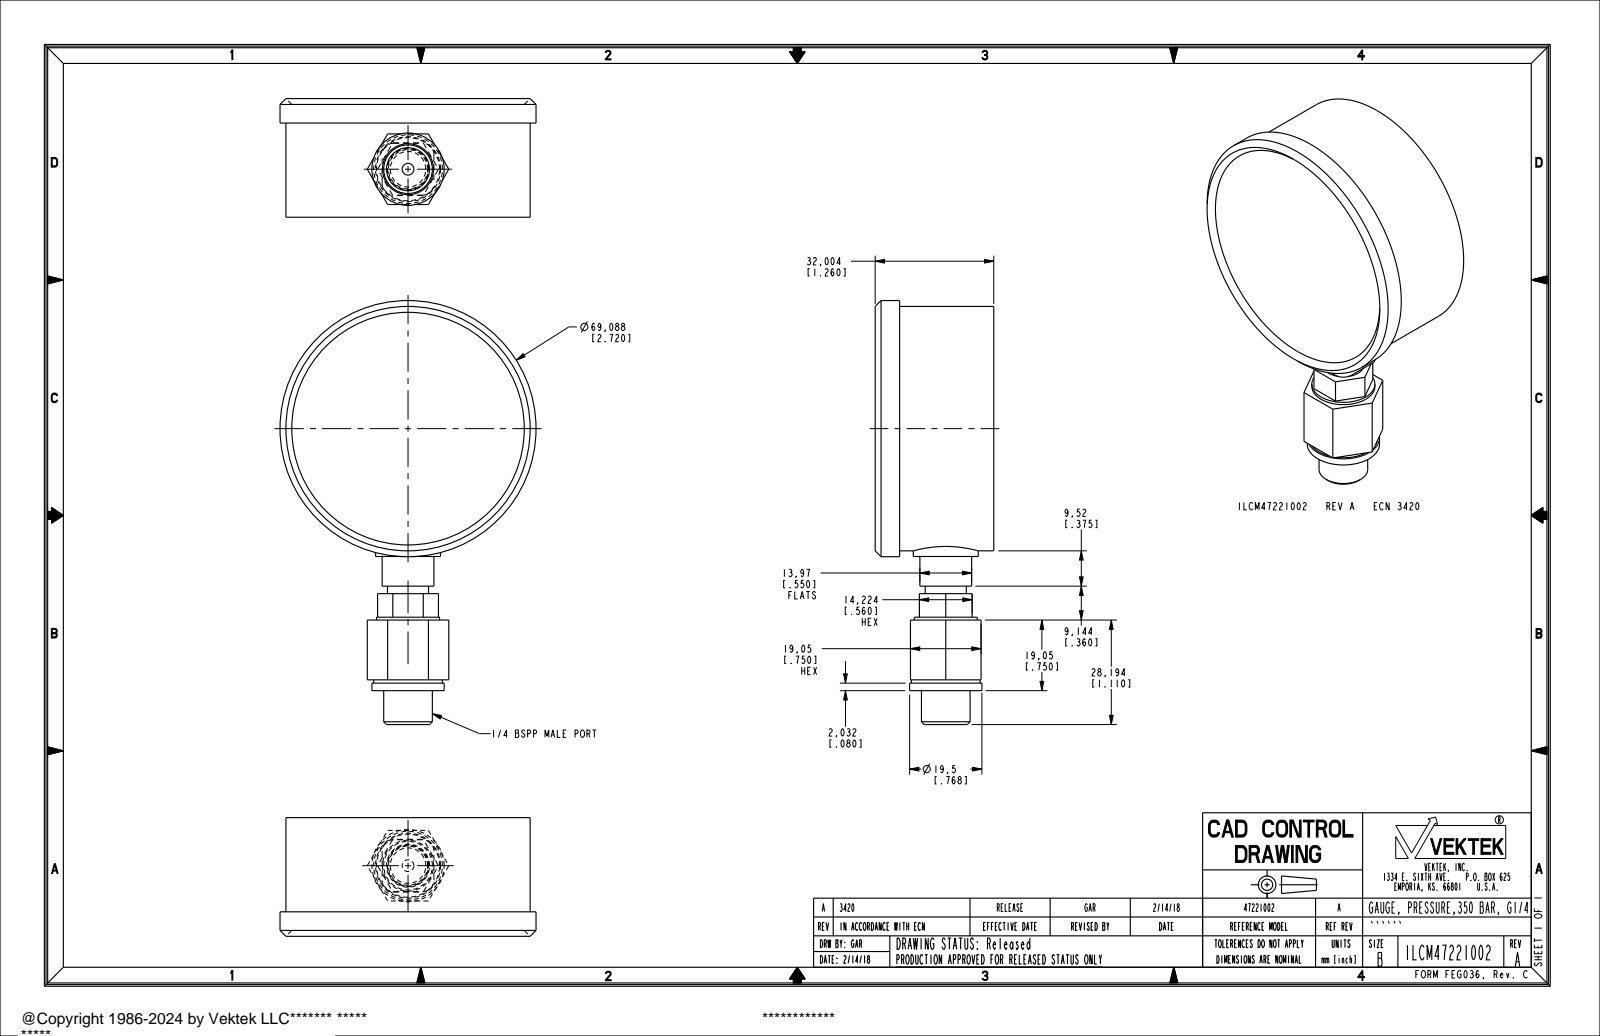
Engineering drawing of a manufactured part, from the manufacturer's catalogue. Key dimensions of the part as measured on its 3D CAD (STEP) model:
Part name (STEP PRODUCT): ILCM47221002
STEP written by: PRO/ENGINEER BY PARAMETRIC TECHNOLOGY CORPORATION, 2013320 (AUTOMOTIVE_DESIGN)
Units: millimetres
Bodies: 1 solid, 69 faces (33 planar, 28 cylindrical, 8 other)
Overall size (bounding box): 114.36 × 69.09 × 32
Volume: 116 101 mm³ · Surface area: 17 951 mm²
Round holes (diameter × count): ⌀3.17 ×1, ⌀11.18 ×1, ⌀13.76 ×1
Round bosses / shafts (diameter × count): ⌀69.09 ×1, ⌀65.91 ×1, ⌀19.5 ×1, ⌀18.54 ×1, ⌀17.53 ×1, ⌀17.02 ×1, ⌀13.13 ×1, ⌀11.1 ×1
Partial cylindrical surfaces — rounded edges, fillets, slot ends (radius × count): R3.05 ×4
Main face-to-face distances: 30.41, 25.4, 19.04, 5.01, 2.92, 2.41, 16.63, 3.42, 22.48, 19.06
